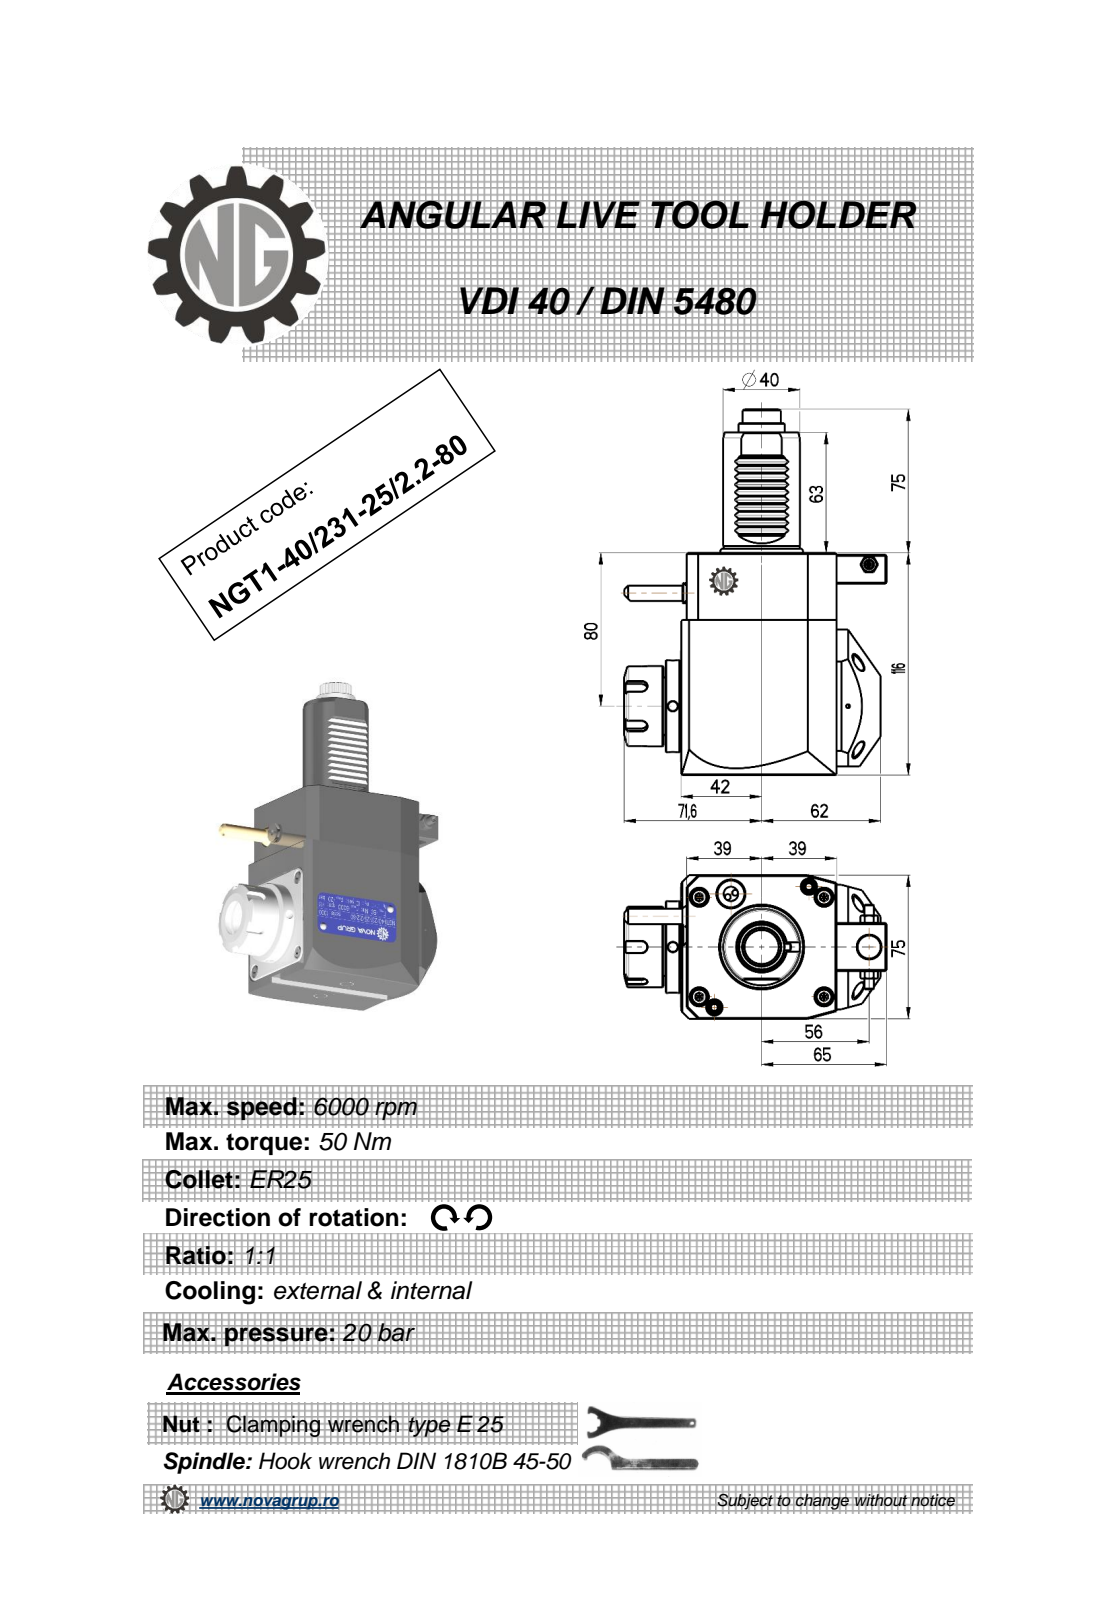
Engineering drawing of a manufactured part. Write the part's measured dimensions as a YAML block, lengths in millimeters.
part_name: "NGT1_40_231_25_2_2_80"
step_written_by: "PRO/ENGINEER BY PARAMETRIC TECHNOLOGY CORPORATION, 2010280 (CONFIG_CONTROL_DESIGN)"
units: millimeters
bodies: {solids: 1, faces: 561, planar: 200, cylindrical: 185, other: 176}
overall_size: [191, 136.6, 76.6]
volume: 877271
surface_area: 70465
round_holes:
  - {diameter: 5, count: 3}
  - {diameter: 3, count: 1}
  - {diameter: 4.2, count: 1}
  - {diameter: 9.5, count: 1}
  - {diameter: 12, count: 1}
  - {diameter: 20.3, count: 1}
round_bosses_or_shafts:
  - {diameter: 48, count: 1}
  - {diameter: 42, count: 1}
  - {diameter: 40, count: 1}
  - {diameter: 37.5, count: 1}
  - {diameter: 33, count: 1}
  - {diameter: 24, count: 1}
  - {diameter: 11.2, count: 1}
  - {diameter: 8.96, count: 1}
partial_cylinders:
  - {radius: 2.08, count: 48}
  - {radius: 0.26, count: 12}
  - {radius: 0.3, count: 10}
  - {radius: 0.22, count: 6}
  - {radius: 3, count: 5}
  - {radius: 9.08, count: 1}
  - {radius: 9.92, count: 1}
  - {radius: 15, count: 1}
face_to_face_distances: [75, 116, 81, 3, 78, 2.8, 80.8, 112, 7.5, 0.5]
hole_center_spacings: [20.3, 61.13, 71.5, 102.25, 126.22]
